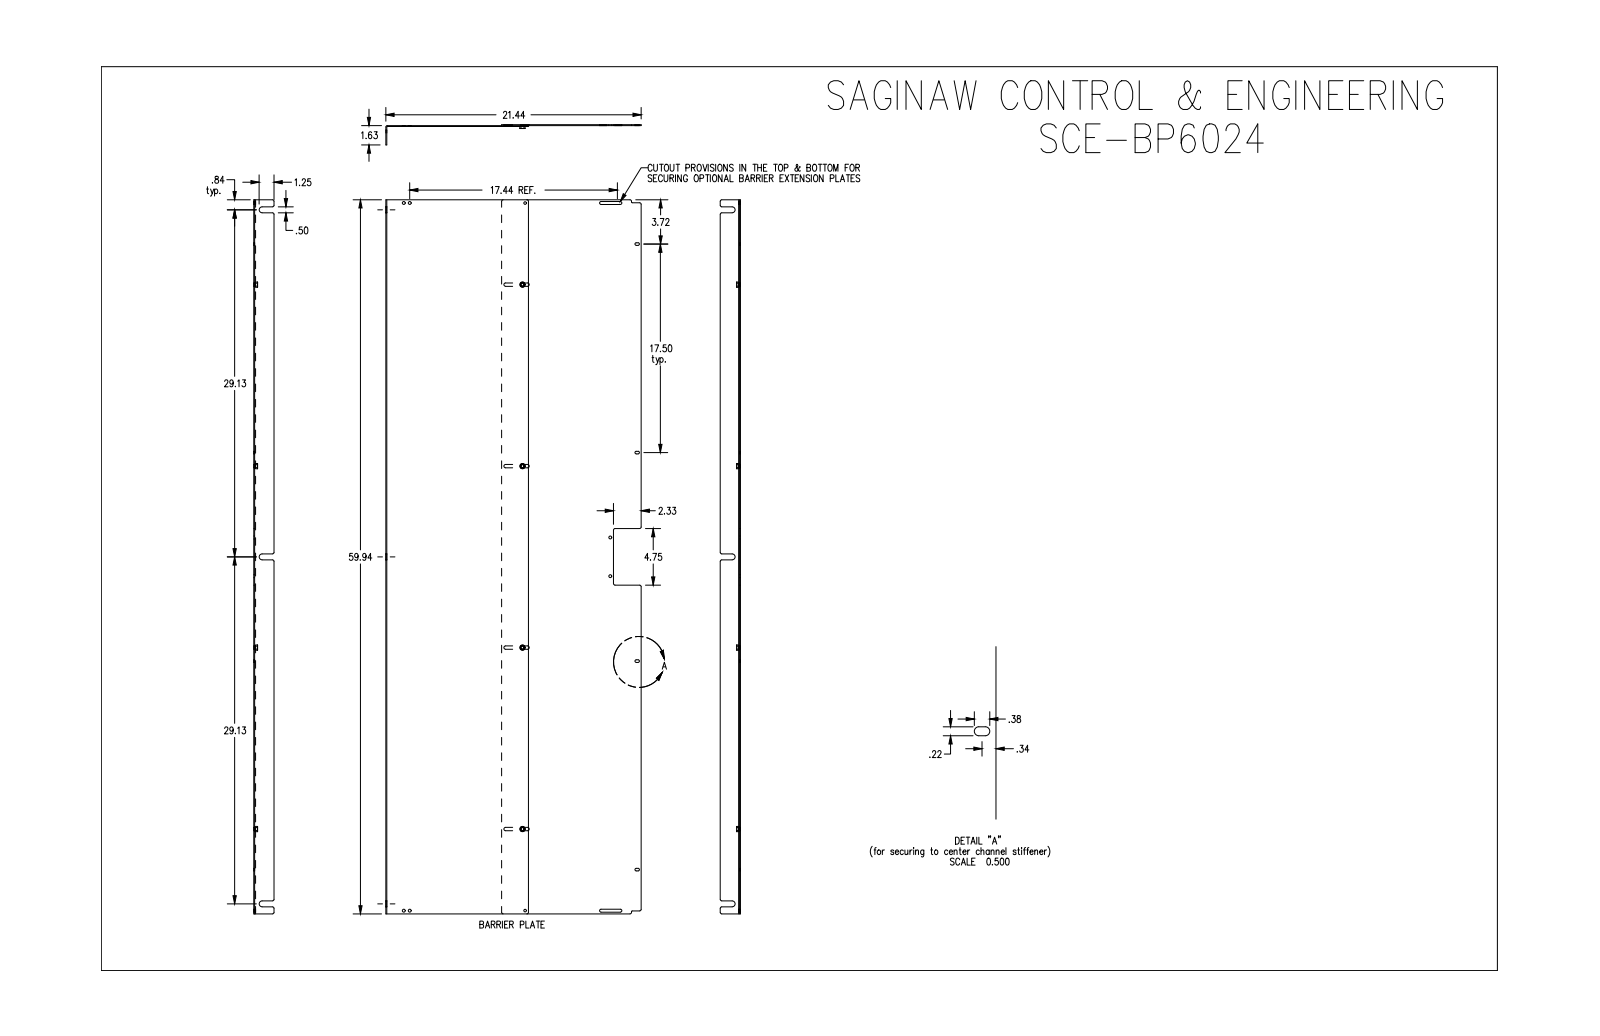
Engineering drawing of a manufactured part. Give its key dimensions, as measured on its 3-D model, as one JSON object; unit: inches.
{"part_name": "SCE-BP6024", "step_written_by": "SolidWorks 2019 (CONFIG_CONTROL_DESIGN)", "units": "inches", "bodies": {"solids": 6, "faces": 146, "planar": 63, "cylindrical": 71, "other": 12}, "overall_size": [59.937, 21.44, 1.7], "volume_in3": 112.1, "surface_area_in2": 3015, "round_holes": [[0.25, 10], [0.344, 4], [0.218, 2]], "round_bosses_or_shafts": [[0.44, 4], [0.343, 4]], "partial_cylinders_radius": [[0.125, 24], [0.109, 8], [0.141, 8], [0.25, 3], [0.062, 2], [0.042, 1], [0.117, 1]], "face_to_face_distances": [0.075, 0.15, 9.72, 11.97, 9.645, 11.895, 2.25, 1.7, 1.625, 1.55], "hole_center_spacings": [15.229, 0.5, 6.847, 9.497, 9.689, 10.189, 11.691, 11.819]}
